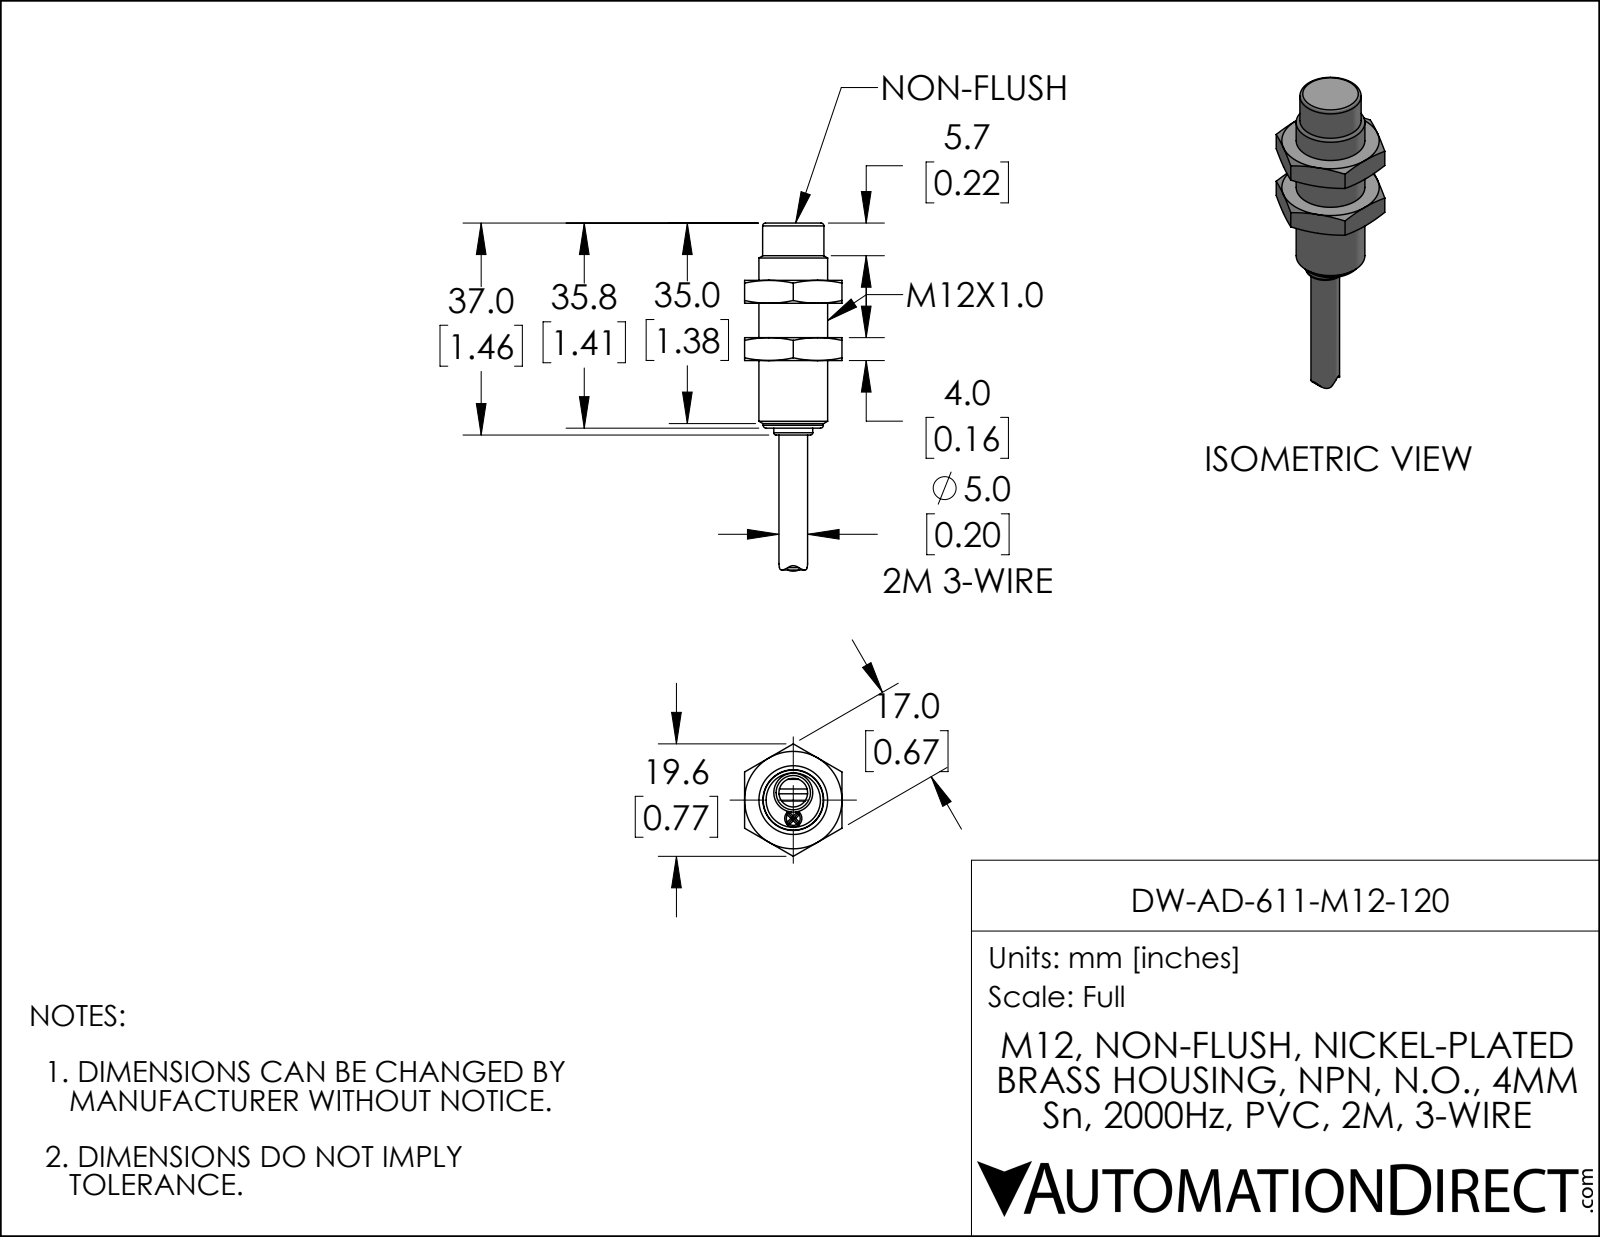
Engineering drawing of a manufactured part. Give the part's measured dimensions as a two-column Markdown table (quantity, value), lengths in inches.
| quantity | value |
| --- | --- |
| part name | DW-AD-611-M12-120 |
| STEP written by | SolidWorks 2019 (AUTOMOTIVE_DESIGN) |
| units | inches |
| bodies | 1 solid, 80 faces (33 planar, 13 cylindrical, 34 other) |
| overall size | 2.392 × 0.773 × 0.669 |
| volume | 0.333 in³ |
| surface area | 4.025 in² |
| round bosses / shafts (diameter × count) | 0.472 × 1, 0.421 × 1, 0.413 × 1, 0.268 × 1, 0.197 × 1, 0.118 × 1 |
| partial cylindrical surfaces (radius × count) | 0.031 × 1, 0.041 × 1, 0.165 × 1, 0.248 × 1, 0.331 × 1 |
| main face-to-face distances | 0.394, 0.157, 0.669, 0.551, 0.236, 0.787, 0.945, 1.409, 1.016, 0.858 |
